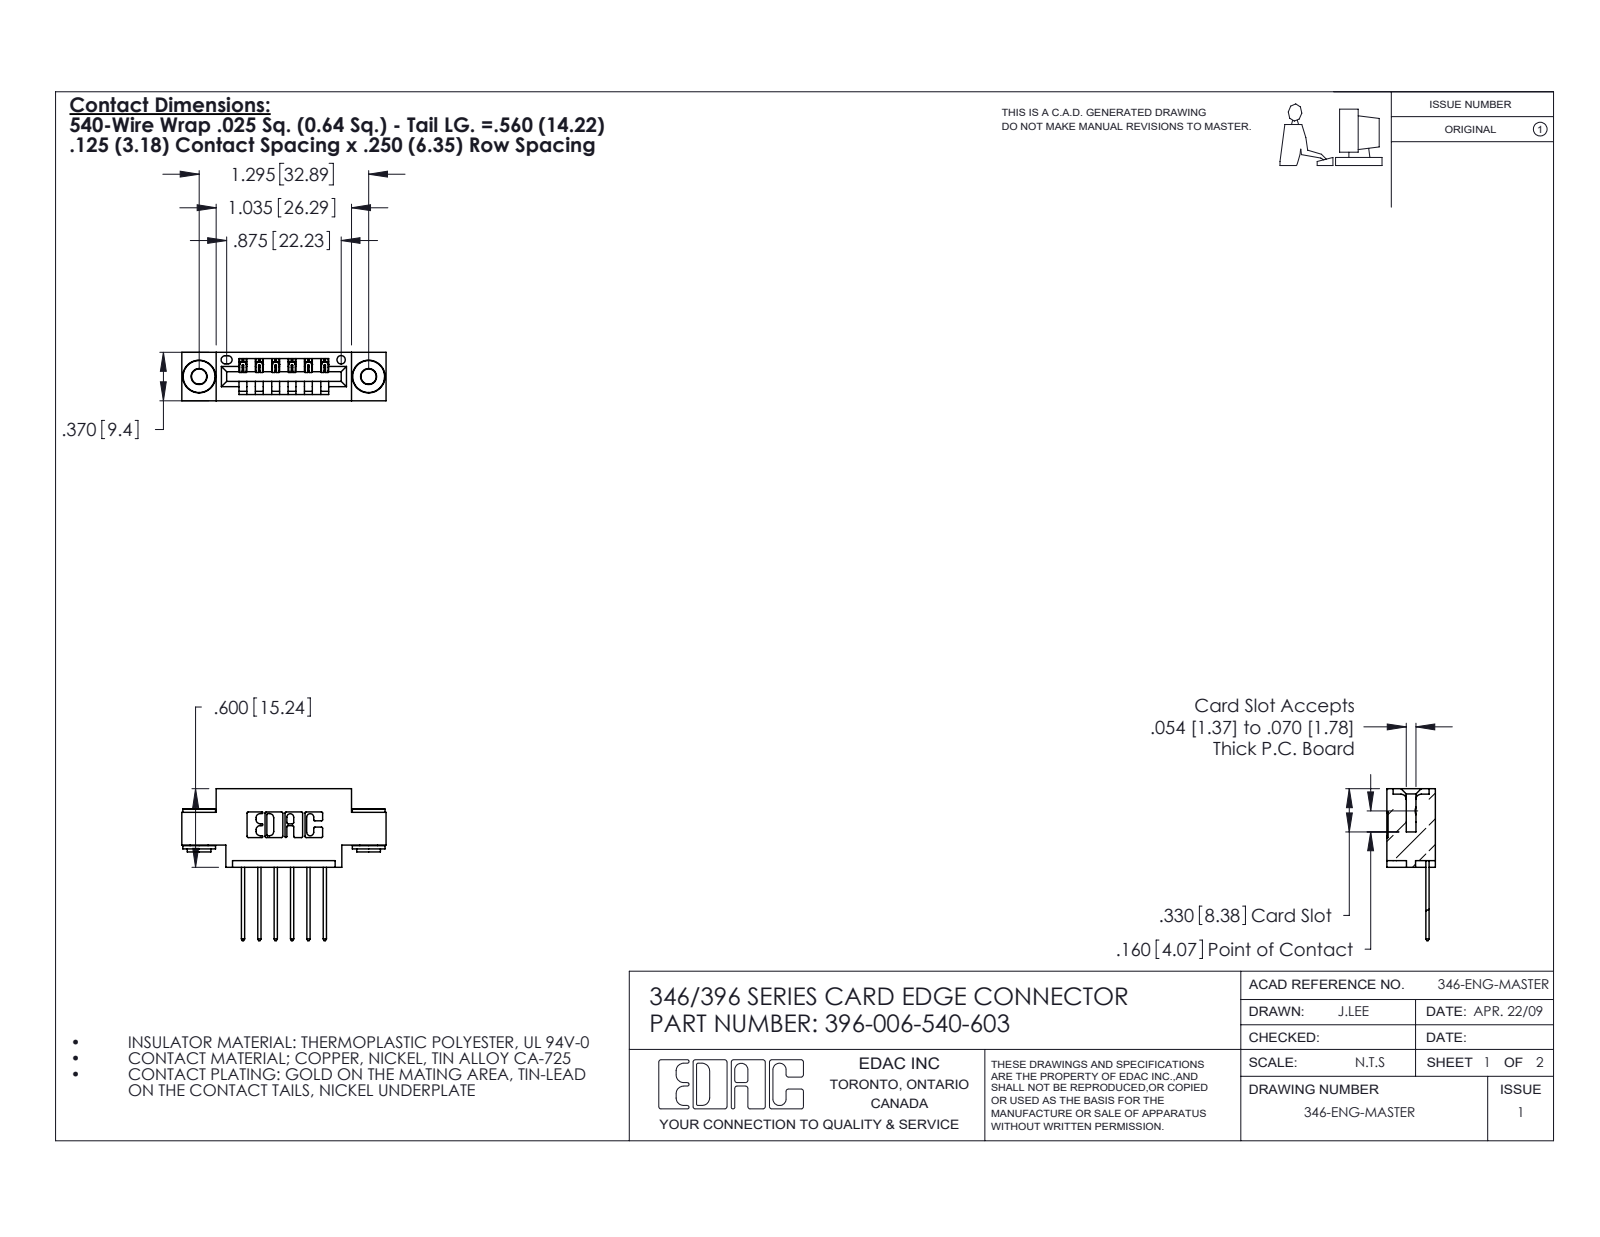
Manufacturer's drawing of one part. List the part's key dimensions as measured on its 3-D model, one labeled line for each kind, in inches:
Part name (STEP PRODUCT): 345-292-001_345-293-140; 396-006-540-603; 346 Part_0.170 Offset - 0.156 Dia-TH; 345-250-002_345-250-002-102
STEP written by: SolidWorks 2020 (CONFIG_CONTROL_DESIGN)
Units: inches
Bodies: 9 solids, 526 faces (344 planar, 174 cylindrical, 8 other)
Overall size (bounding box): 1.56 × 1.16 × 0.37
Volume: 0.207 in³ · Surface area: 6.714 in²
Round holes (diameter × count): ⌀0.116 ×2, ⌀0.156 ×2, ⌀0.064 ×1
Round bosses / shafts (diameter × count): ⌀0.25 ×2, ⌀0.18 ×2, ⌀0.136 ×2
Partial cylindrical surfaces — rounded edges, fillets, slot ends (radius × count): R0.01 ×22, R0.006 ×12, R0.01 ×12, R0.007 ×6, R0.031 ×6, R0.026 ×3, R0.031 ×2, R0.04 ×2
Main face-to-face distances: 0.25, 0.37, 0.048, 0.322, 0.025, 0.222, 0.072, 0.298, 0.148, 0.1
Hole centre spacings: 0.246, 1.092, 1.295
